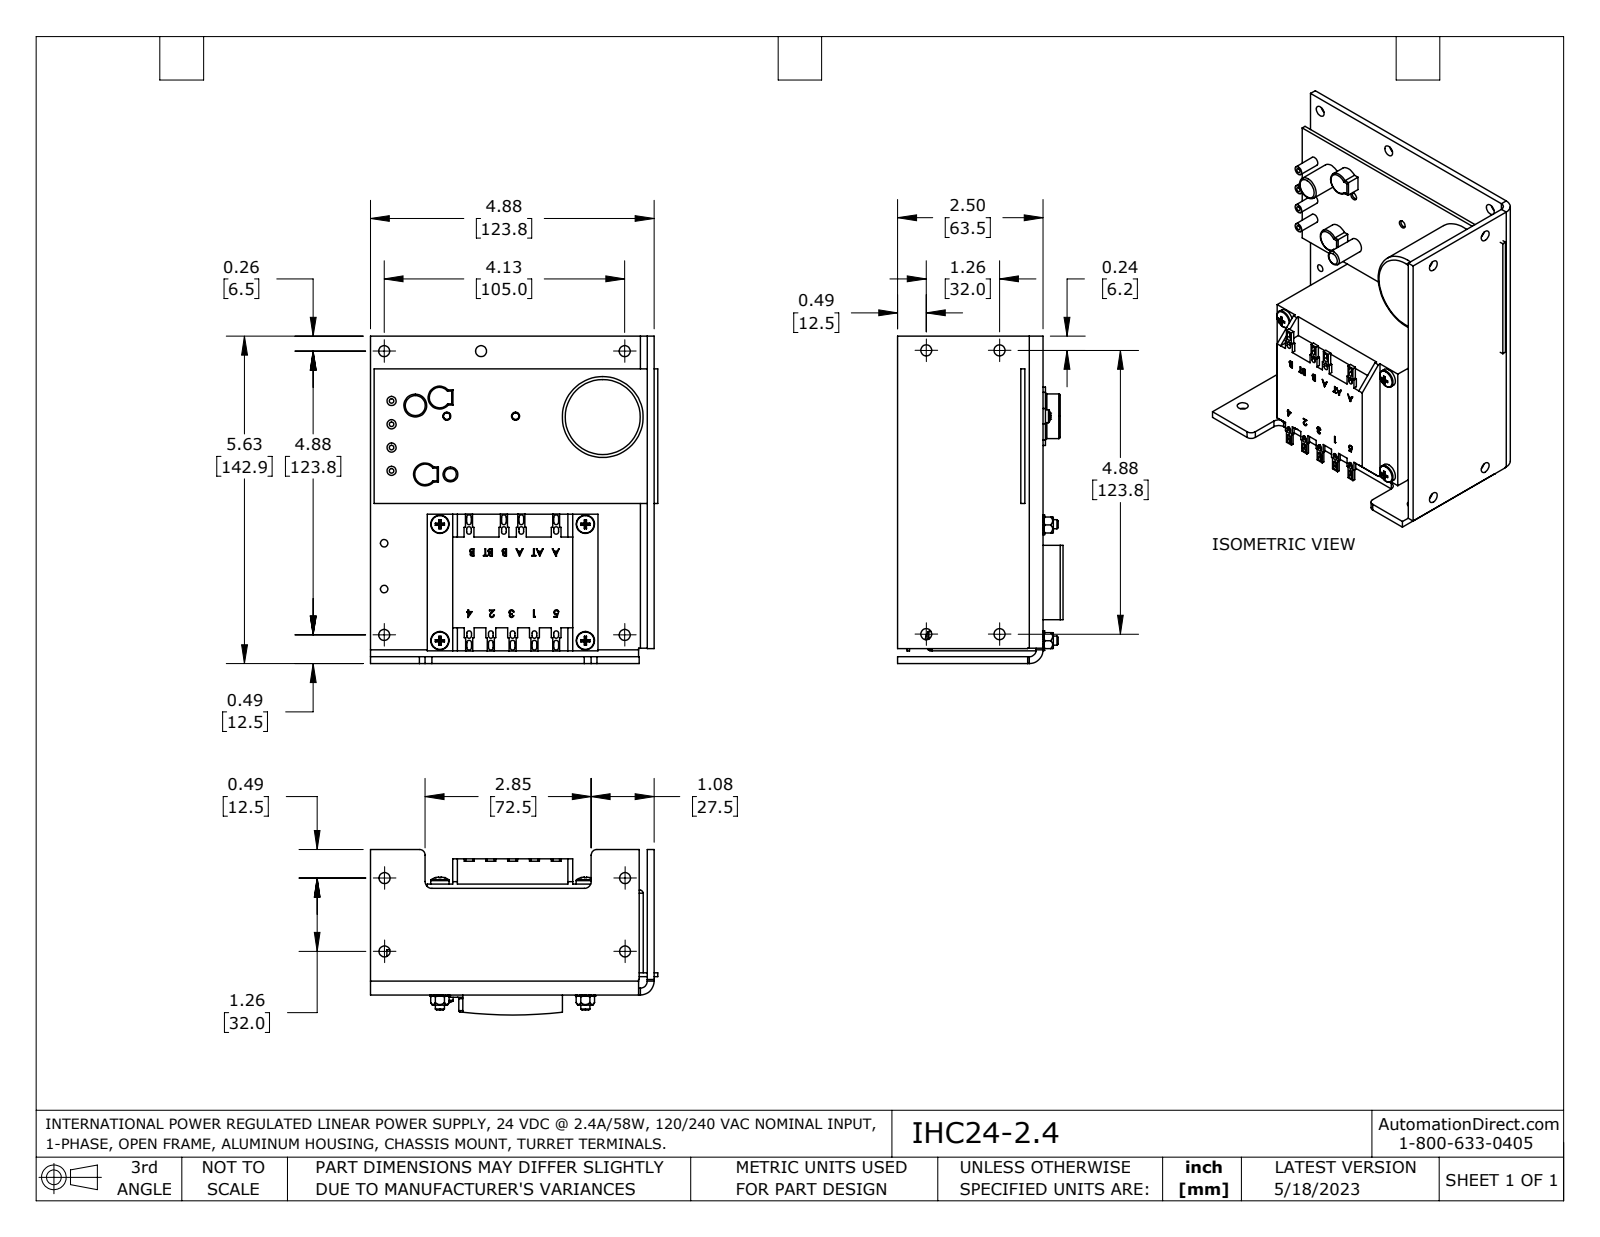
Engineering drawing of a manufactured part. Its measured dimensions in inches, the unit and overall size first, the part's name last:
Units: inches
Overall size (bounding box): 5.625 × 4.937 × 2.844
Round holes (diameter × count): ⌀0.189 ×13, ⌀0.13 ×6, ⌀0.079 ×4, ⌀0.157 ×4, ⌀0.169 ×4, ⌀0.115 ×2, ⌀0.12 ×2, ⌀0.128 ×2, ⌀0.138 ×2
Round bosses / shafts (diameter × count): ⌀0.157 ×6, ⌀0.315 ×4, ⌀0.25 ×2, ⌀0.22 ×2, ⌀0.118 ×2, ⌀1.39 ×1, ⌀0.768 ×1, ⌀0.394 ×1
Partial cylindrical surfaces — rounded edges, fillets, slot ends (radius × count): R0.04 ×36, R0.02 ×6, R0.118 ×4, R0.126 ×4, R0.167 ×4, R0.1 ×2, R0.162 ×2, R0.197 ×2
Main face-to-face distances: 0.118, 0.197, 0.315, 0.067, 0.264, 0.382, 0.22, 0.102, 2.346, 2.449
Hole centre spacings: 2.5, 1.26, 4.134, 0.4, 0.787, 0.8, 1.988, 2
Volume: 23.36 in³ · Surface area: 181.2 in²
Bodies: 18 solids, 893 faces (559 planar, 220 cylindrical, 114 other)
Part name (STEP PRODUCT): IHC24-2.4
STEP written by: SolidWorks 2021 (AUTOMOTIVE_DESIGN)
